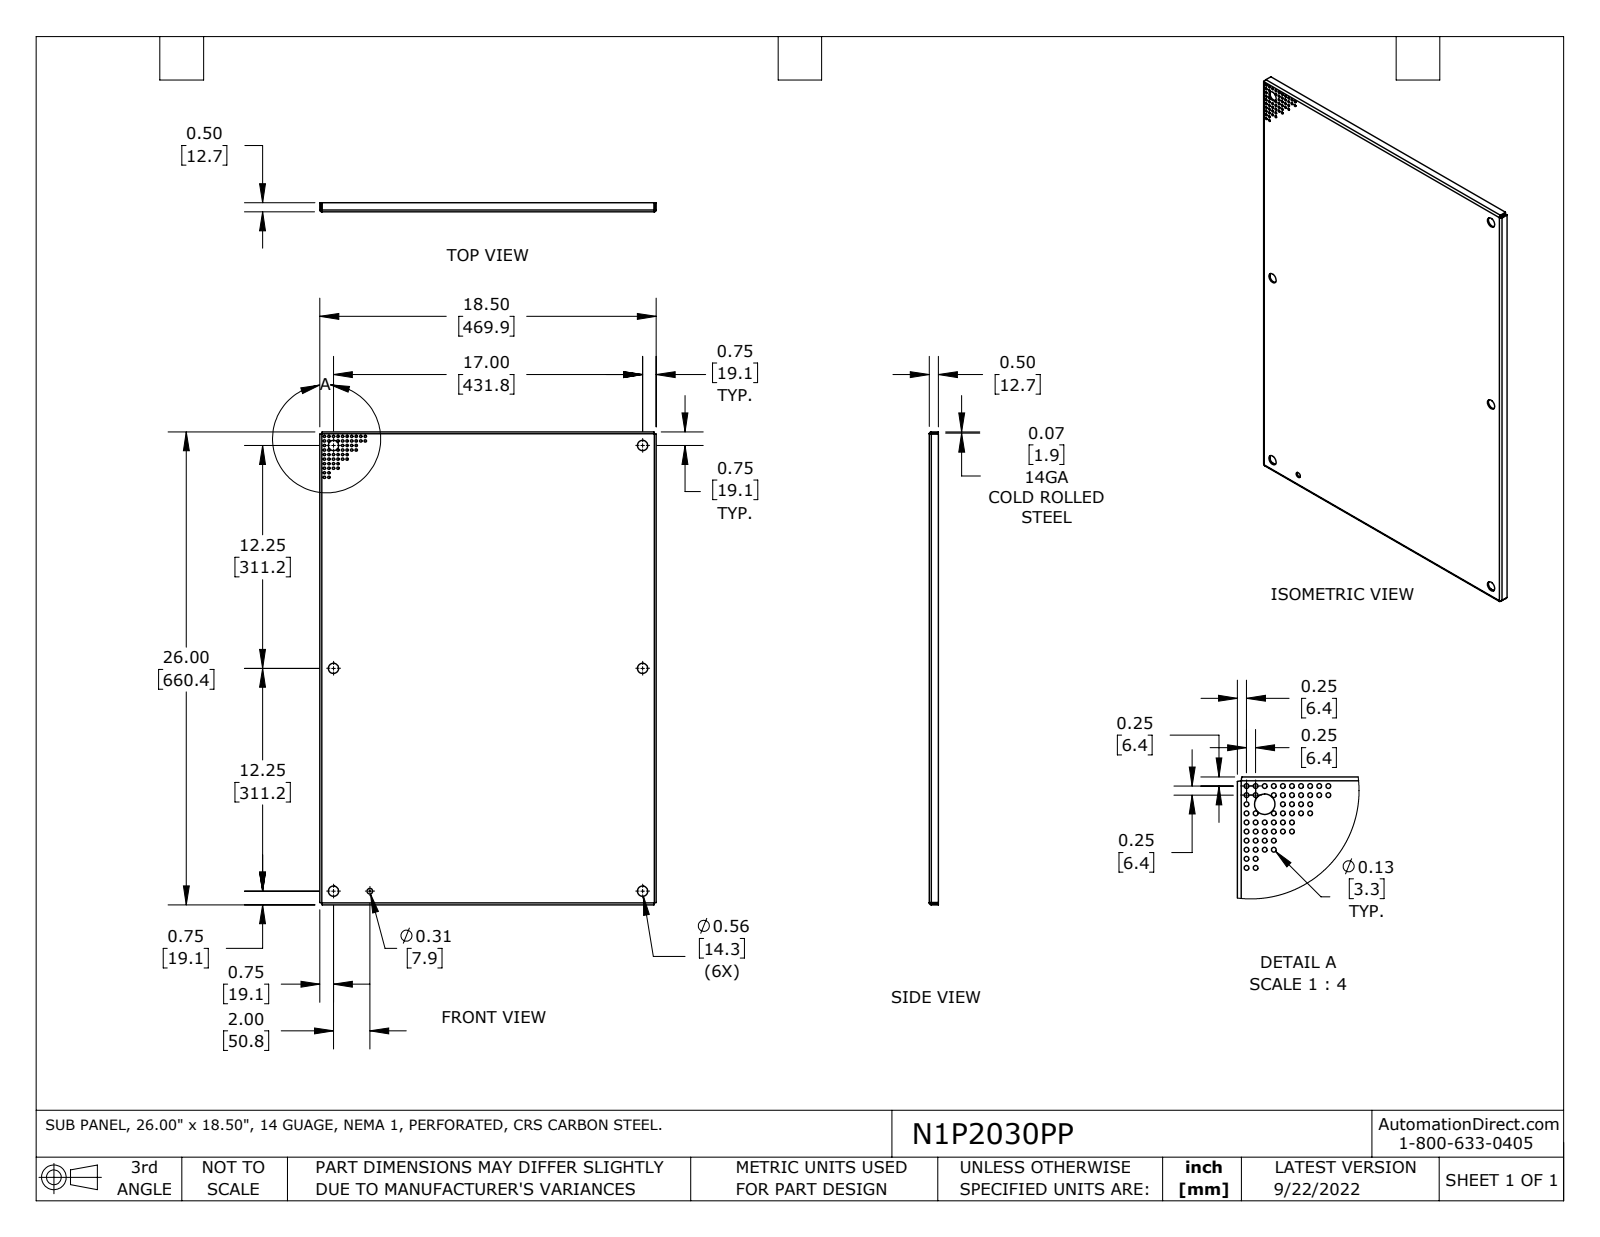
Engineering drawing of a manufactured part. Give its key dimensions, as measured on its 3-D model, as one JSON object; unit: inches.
{"part_name": "N1P2030PP", "step_written_by": "SolidWorks 2021 (AUTOMOTIVE_DESIGN)", "units": "inches", "bodies": {"solids": 1, "faces": 162, "planar": 22, "cylindrical": 132, "other": 8}, "overall_size": [26, 18.5, 0.5], "volume_in3": 38, "surface_area_in2": 1036, "round_holes": [[0.13, 55], [0.563, 6], [0.312, 1]], "partial_cylinders_radius": [[0.031, 4], [0.105, 4]], "face_to_face_distances": [0.074, 18.426, 25.926, 18.5, 18.352, 25.852, 26, 0.426, 0.5, 0.126], "hole_center_spacings": [0.791, 0.25, 0.559, 1.25, 0.902, 0.75, 0.5, 0.354]}
